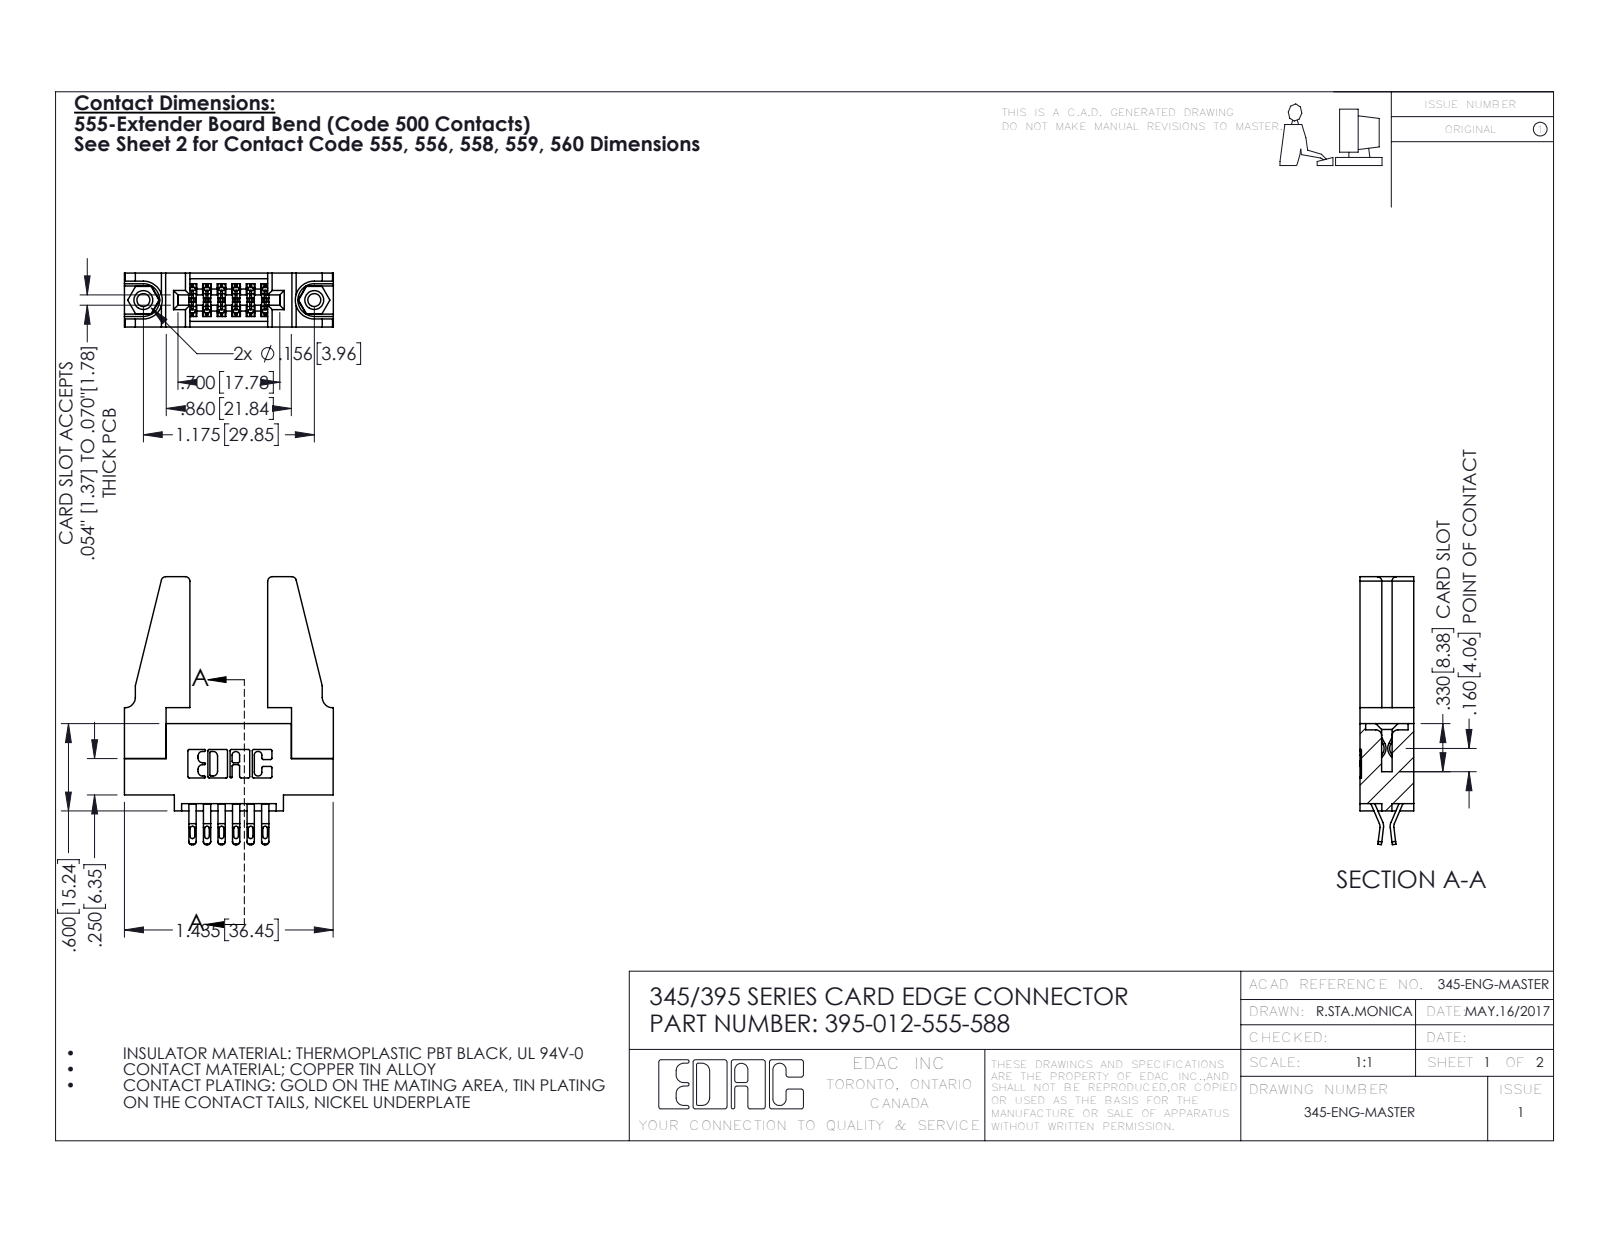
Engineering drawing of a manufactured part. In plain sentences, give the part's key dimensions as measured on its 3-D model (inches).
The part is named "345 Part_0.110 Offset - 0.156 Dia-TH; 345-292-001_555 Tail; 345-250-001_345-250-001-102; 395-012-555-588 (+1 more)". Its 3-D file was written by "SolidWorks 2016 (CONFIG_CONTROL_DESIGN)". It is 17 solids with 926 faces: 528 planar, 382 cylindrical and 16 other. Overall it measures 1.842 by 1.436 by 0.37 inches. Its volume is 0.392 cubic inches and its surface area 11.35 square inches. Round holes: 2 of diameter 0.089, 2 of diameter 0.125, 2 of diameter 0.156, 1 of diameter 0.064. Round bosses or shafts: 2 of diameter 0.155. Partial cylindrical surfaces (rounded edges, fillets, slot ends): 30 of radius 0.016, 24 of radius 0.02, 22 of radius 0.01, 18 of radius 0.006, 8 of radius 0.03, 6 of radius 0.007, 6 of radius 0.031, 3 of radius 0.026. The main face-to-face distances are 0.37, 0.072, 0.298, 0.2, 0.025, 0.15, 0.148, 0.225, 0.098, 0.272. The hole center spacings are 0.27, 0.946, 1.175.
